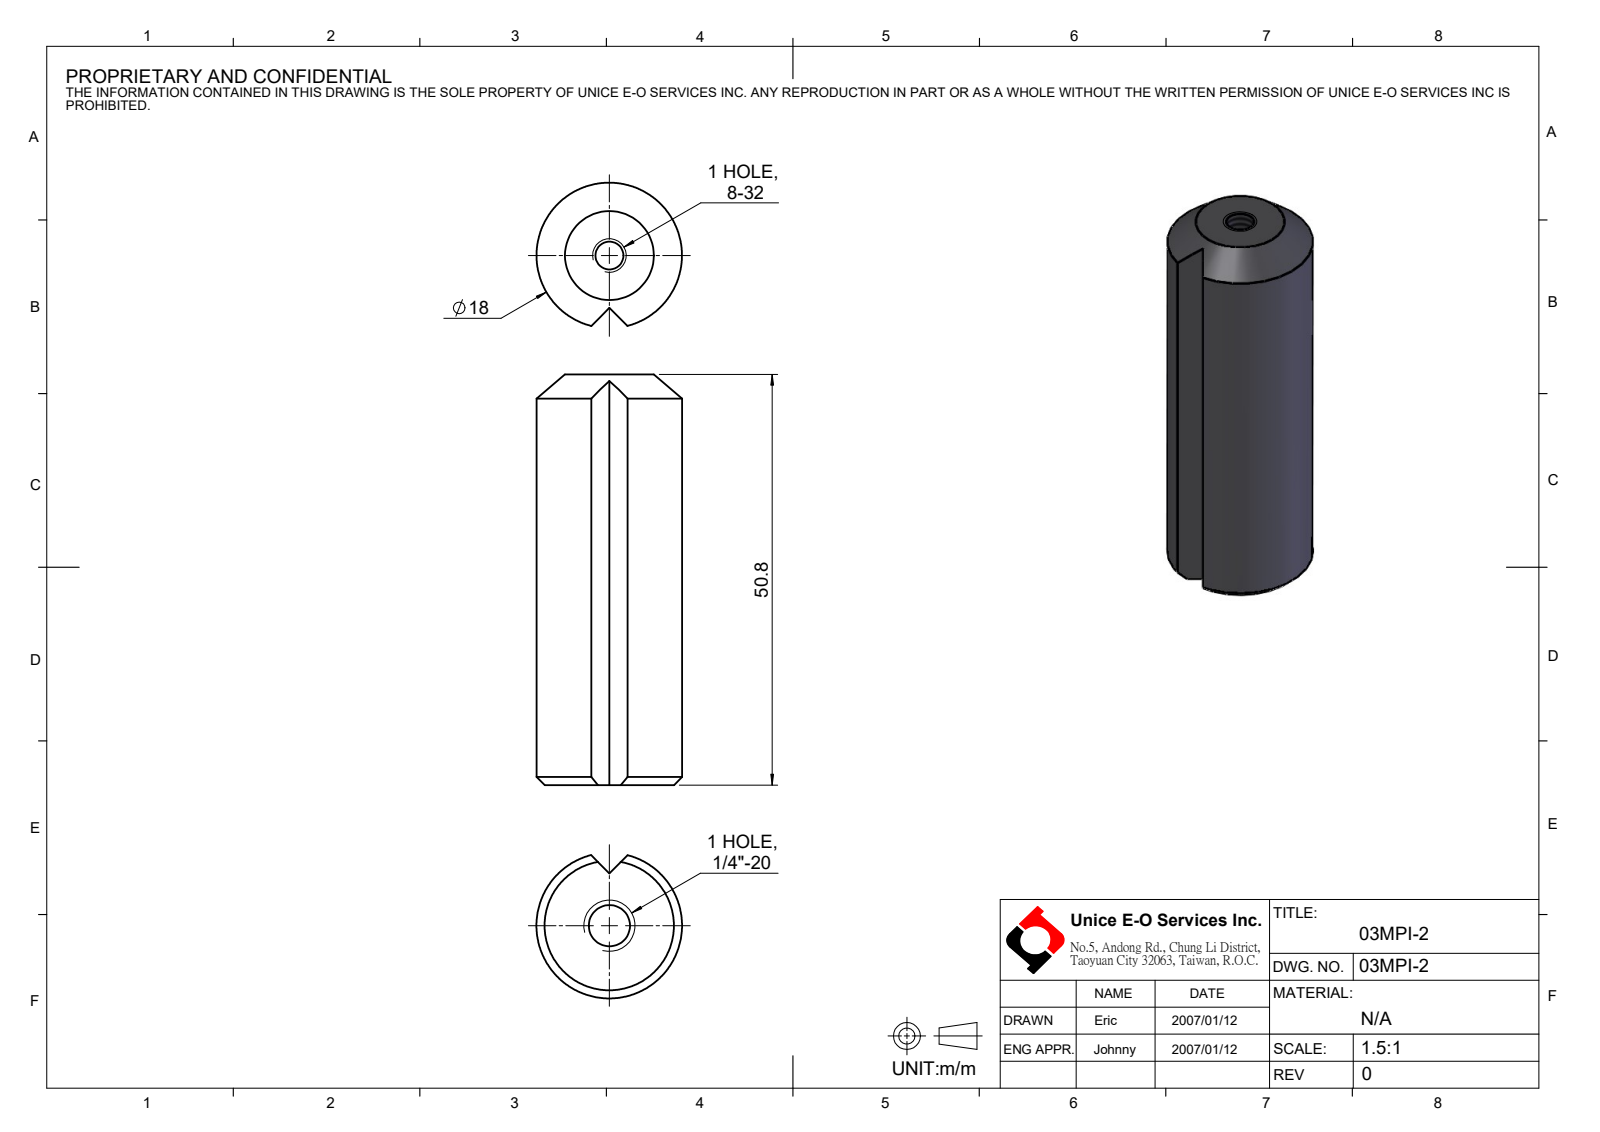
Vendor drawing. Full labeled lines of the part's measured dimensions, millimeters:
Part name (STEP PRODUCT): 03MPI-2
STEP written by: SolidWorks 2016 (CONFIG_CONTROL_DESIGN)
Units: millimetres
Bodies: 1 solid, 20 faces (4 planar, 7 cylindrical, 9 other)
Overall size (bounding box): 50.8 × 18 × 17.71
Volume: 11 962 mm³ · Surface area: 3 649 mm²
Round holes (diameter × count): ⌀3.45 ×1, ⌀5.11 ×1
Round bosses / shafts (diameter × count): ⌀18 ×1
Main face-to-face distances: 50.8
